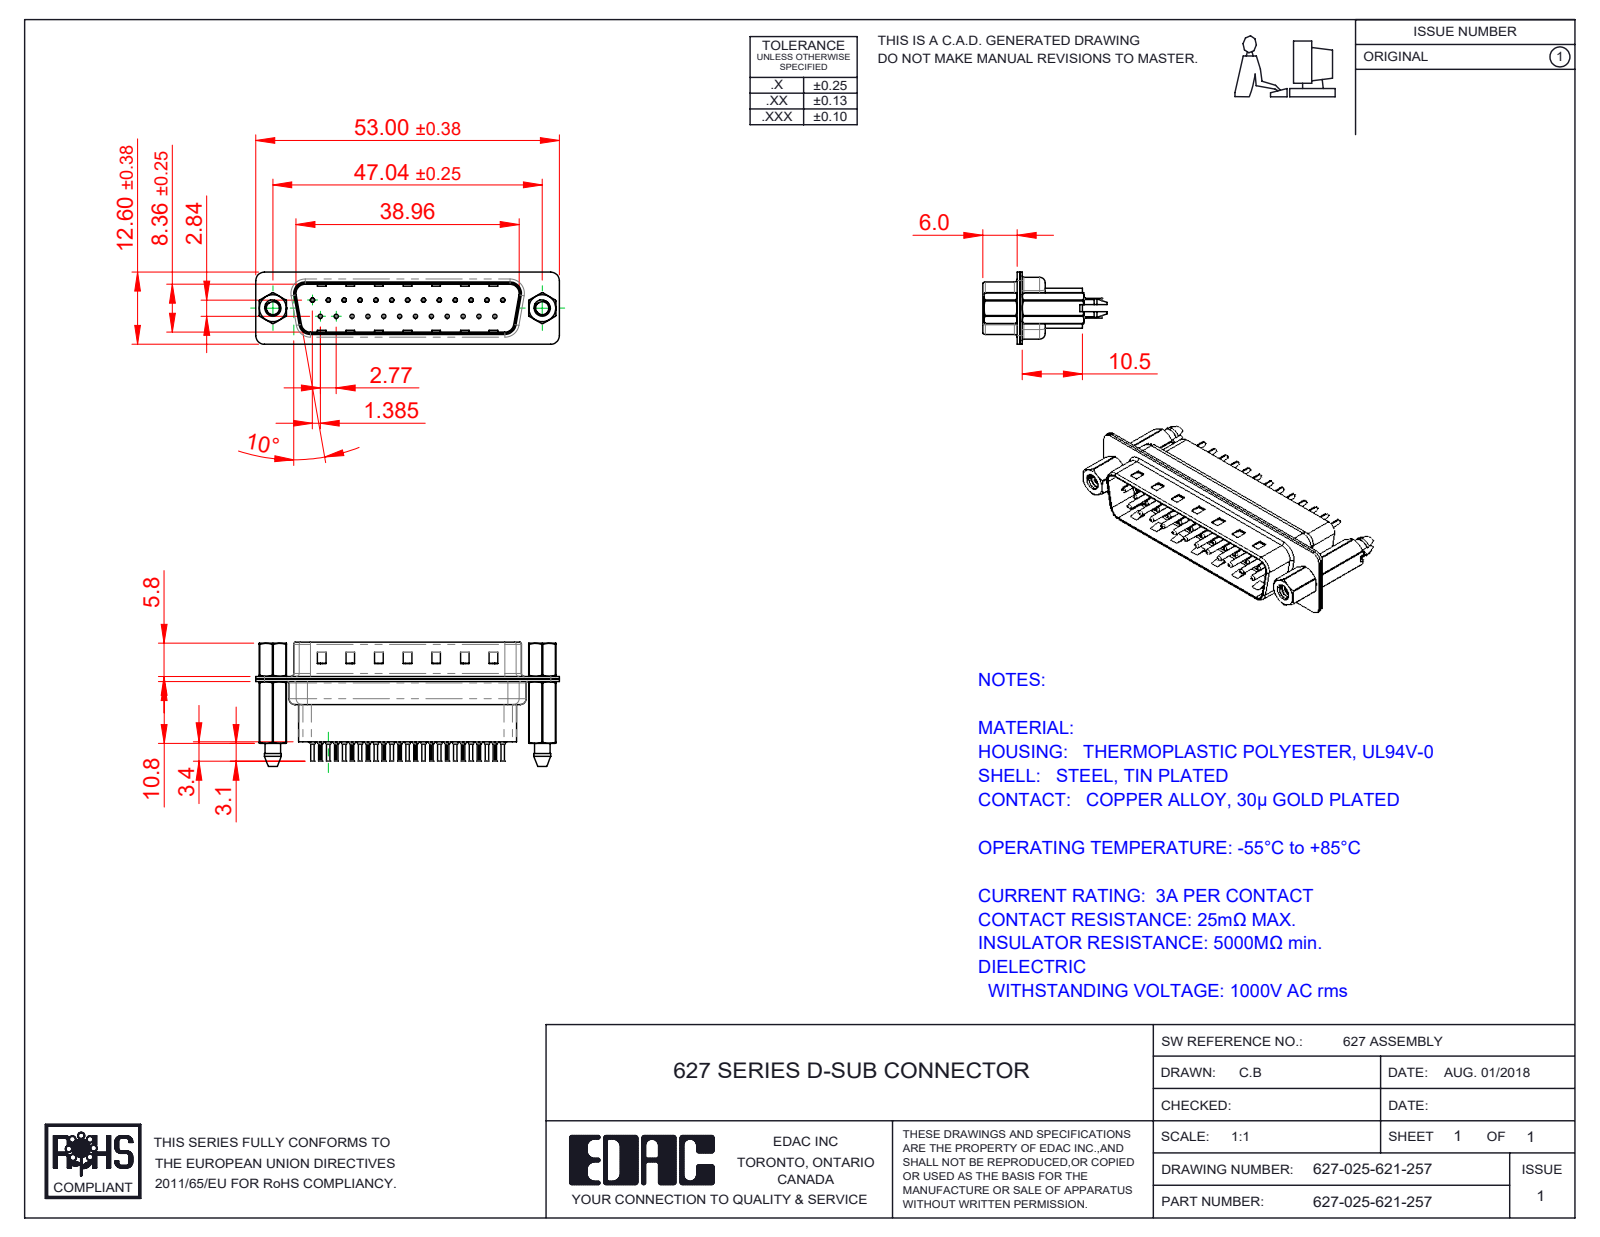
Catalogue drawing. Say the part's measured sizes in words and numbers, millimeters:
The part is named "627 4-40 Threaded Boardlock_HP; 627 4-40 Hex Standoff; 627 Contact Row 1_21H; 627 Shell Front_25 Contacts (+4 more)". Its 3-D file was written by "SolidWorks 2020 (CONFIG_CONTROL_DESIGN)". It is 32 solids with 3066 faces: 825 planar, 1202 cylindrical and 1039 other. Overall it measures 53 by 21.7 by 12.6 millimeters. Its volume is 4 261 cubic millimeters and its surface area 10 842 square millimeters. Round holes: 25 of diameter 0.2, 25 of diameter 0.35, 25 of diameter 1.1, 25 of diameter 1.6, 2 of diameter 2.26, 2 of diameter 2.29, 2 of diameter 4, 2 of diameter 4.8. Round bosses or shafts: 25 of diameter 2, 25 of diameter 1.5, 25 of diameter 0.75, 25 of diameter 0.6, 2 of diameter 4.9, 2 of diameter 2.79. Partial cylindrical surfaces (rounded edges, fillets, slot ends): 50 of radius 0.1, 18 of radius 1.5, 12 of radius 2, 10 of radius 1.6, 8 of radius 0.5, 4 of radius 0.25, 4 of radius 0.6, 4 of radius 0.65. The main face-to-face distances are 0.4, 0.45, 0.82, 9.58, 0.68, 7.68, 1.5, 0.9, 1.08, 8.08. The hole center spacings are 3.16, 8.31, 2.77, 5.54, 11.08, 16.62, 5.03, 5.04.
